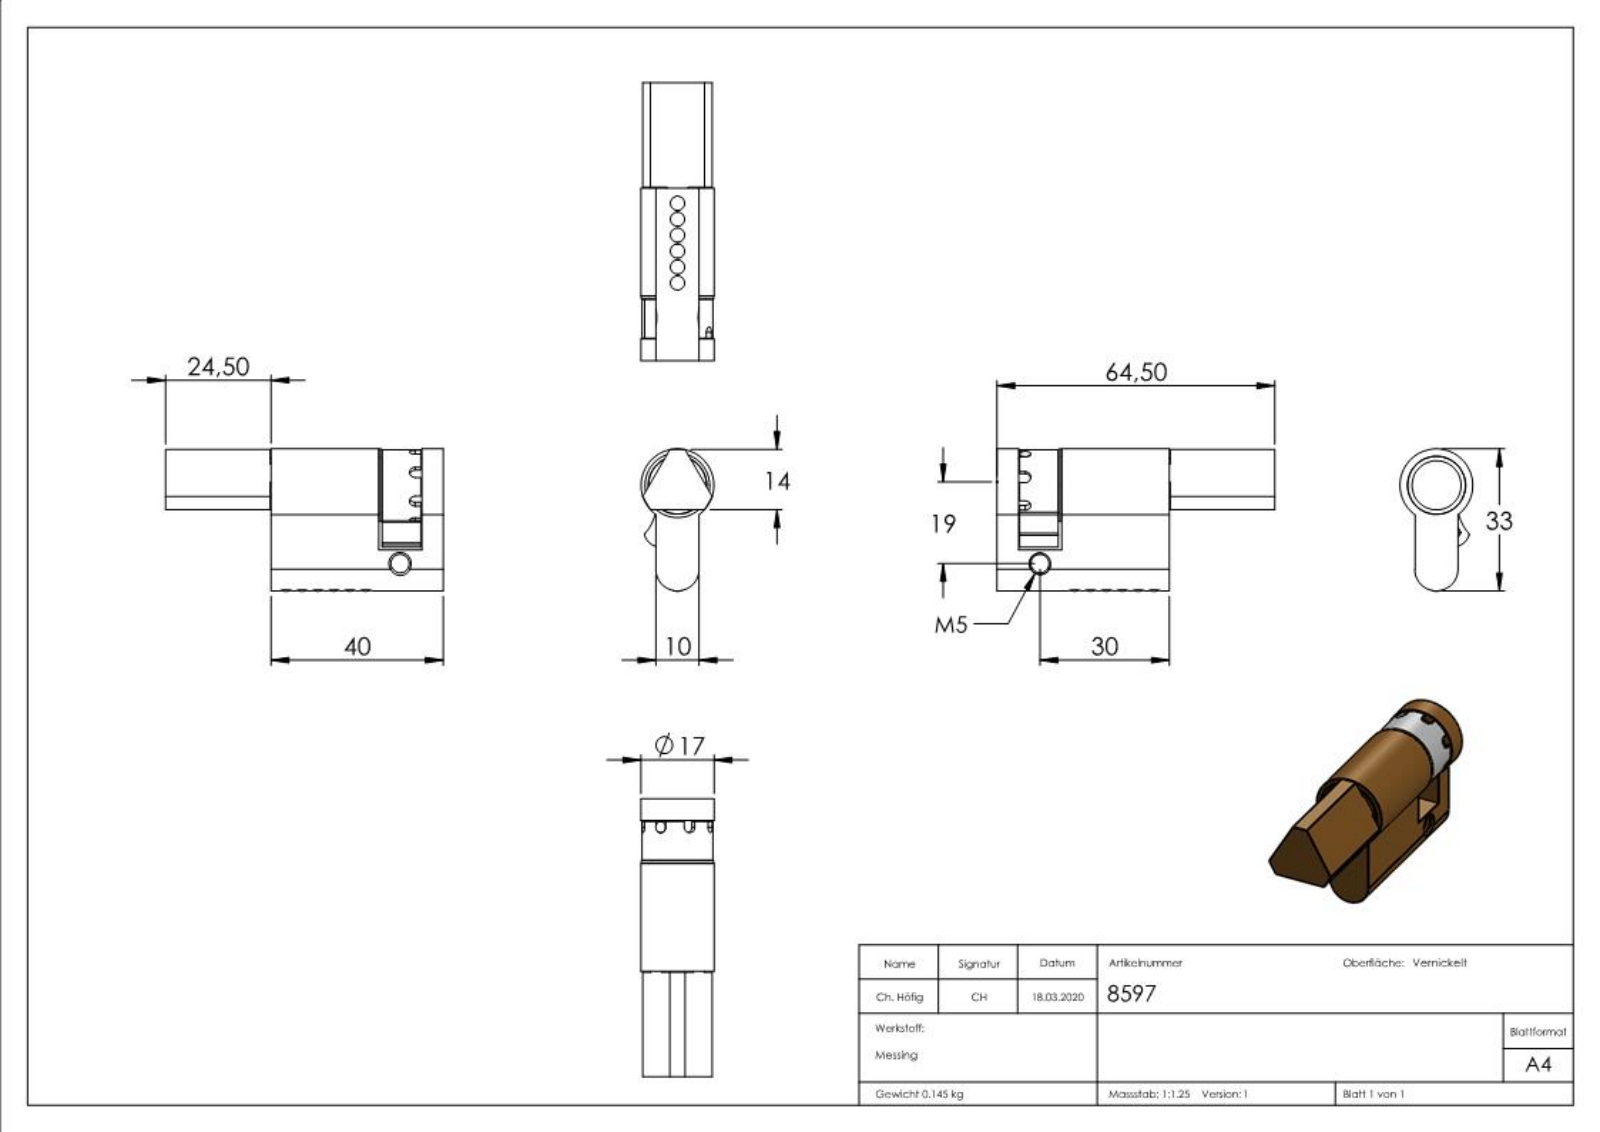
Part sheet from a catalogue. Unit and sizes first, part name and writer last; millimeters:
Units: millimetres
Overall size (bounding box): 64.5 × 33.1 × 17
Round holes (diameter × count): ⌀3.3 ×6, ⌀2.6 ×3, ⌀4.2 ×1, ⌀12.7 ×1, ⌀13.5 ×1, ⌀15 ×1
Round bosses / shafts (diameter × count): ⌀17 ×1, ⌀16.8 ×1, ⌀16.5 ×1, ⌀13.4 ×1
Partial cylindrical surfaces — rounded edges, fillets, slot ends (radius × count): R1.3 ×5, R0.5 ×4, R11 ×2, R12.3 ×2, R2 ×1, R4 ×1, R5 ×1, R6.2 ×1
Main face-to-face distances: 10, 14, 25, 0.7, 24.5, 40, 35, 9.3, 5, 15
Hole centre spacings: 3.7, 7.4, 11.1, 14.8, 18.5
Volume: 17 202 mm³ · Surface area: 10 974 mm²
Bodies: 10 solids, 277 faces (123 planar, 61 cylindrical, 93 other)
Part name (STEP PRODUCT): 859X Teil2_8597 Teil2; 859X Teil3; 859X Teil1; 859X Teil2 (+5 more)
STEP written by: SolidWorks 2015 (CONFIG_CONTROL_DESIGN)
